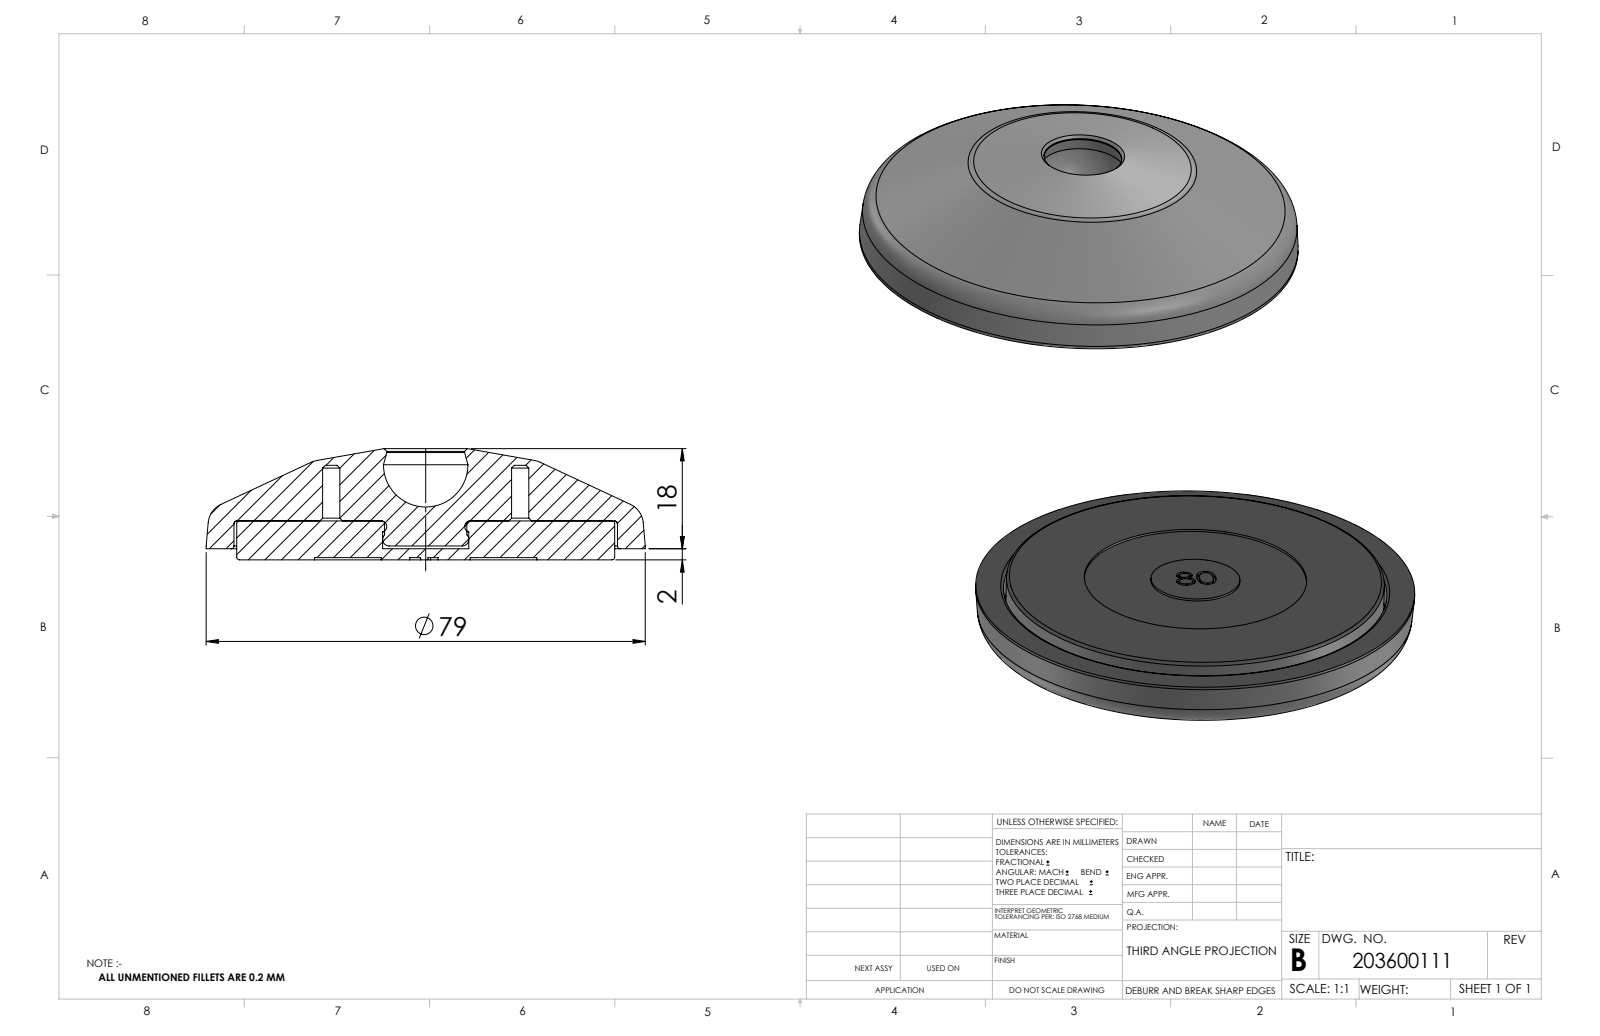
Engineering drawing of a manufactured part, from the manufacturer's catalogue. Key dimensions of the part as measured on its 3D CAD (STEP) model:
Part name (STEP PRODUCT): 203600111_c_1
STEP written by: SolidWorks 2014 (CONFIG_CONTROL_DESIGN)
Units: millimetres
Bodies: 2 solids, 520 faces (91 planar, 106 cylindrical, 323 other)
Overall size (bounding box): 79 × 79 × 24.2
Volume: 58 294 mm³ · Surface area: 25 468 mm²
Round holes (diameter × count): ⌀3.1 ×2, ⌀14 ×1, ⌀15.5 ×1, ⌀40 ×1, ⌀69 ×1
Round bosses / shafts (diameter × count): ⌀79 ×1, ⌀68 ×1, ⌀16 ×1, ⌀14.8 ×1
Partial cylindrical surfaces — rounded edges, fillets, slot ends (radius × count): R0.3 ×24, R0.5 ×24, R3.25 ×2, R21 ×1, R24 ×1
Main face-to-face distances: 7, 2, 5, 0.4, 1.6, 6.6, 3, 2.5, 2.1, 0.5
Hole centre spacings: 17, 34
